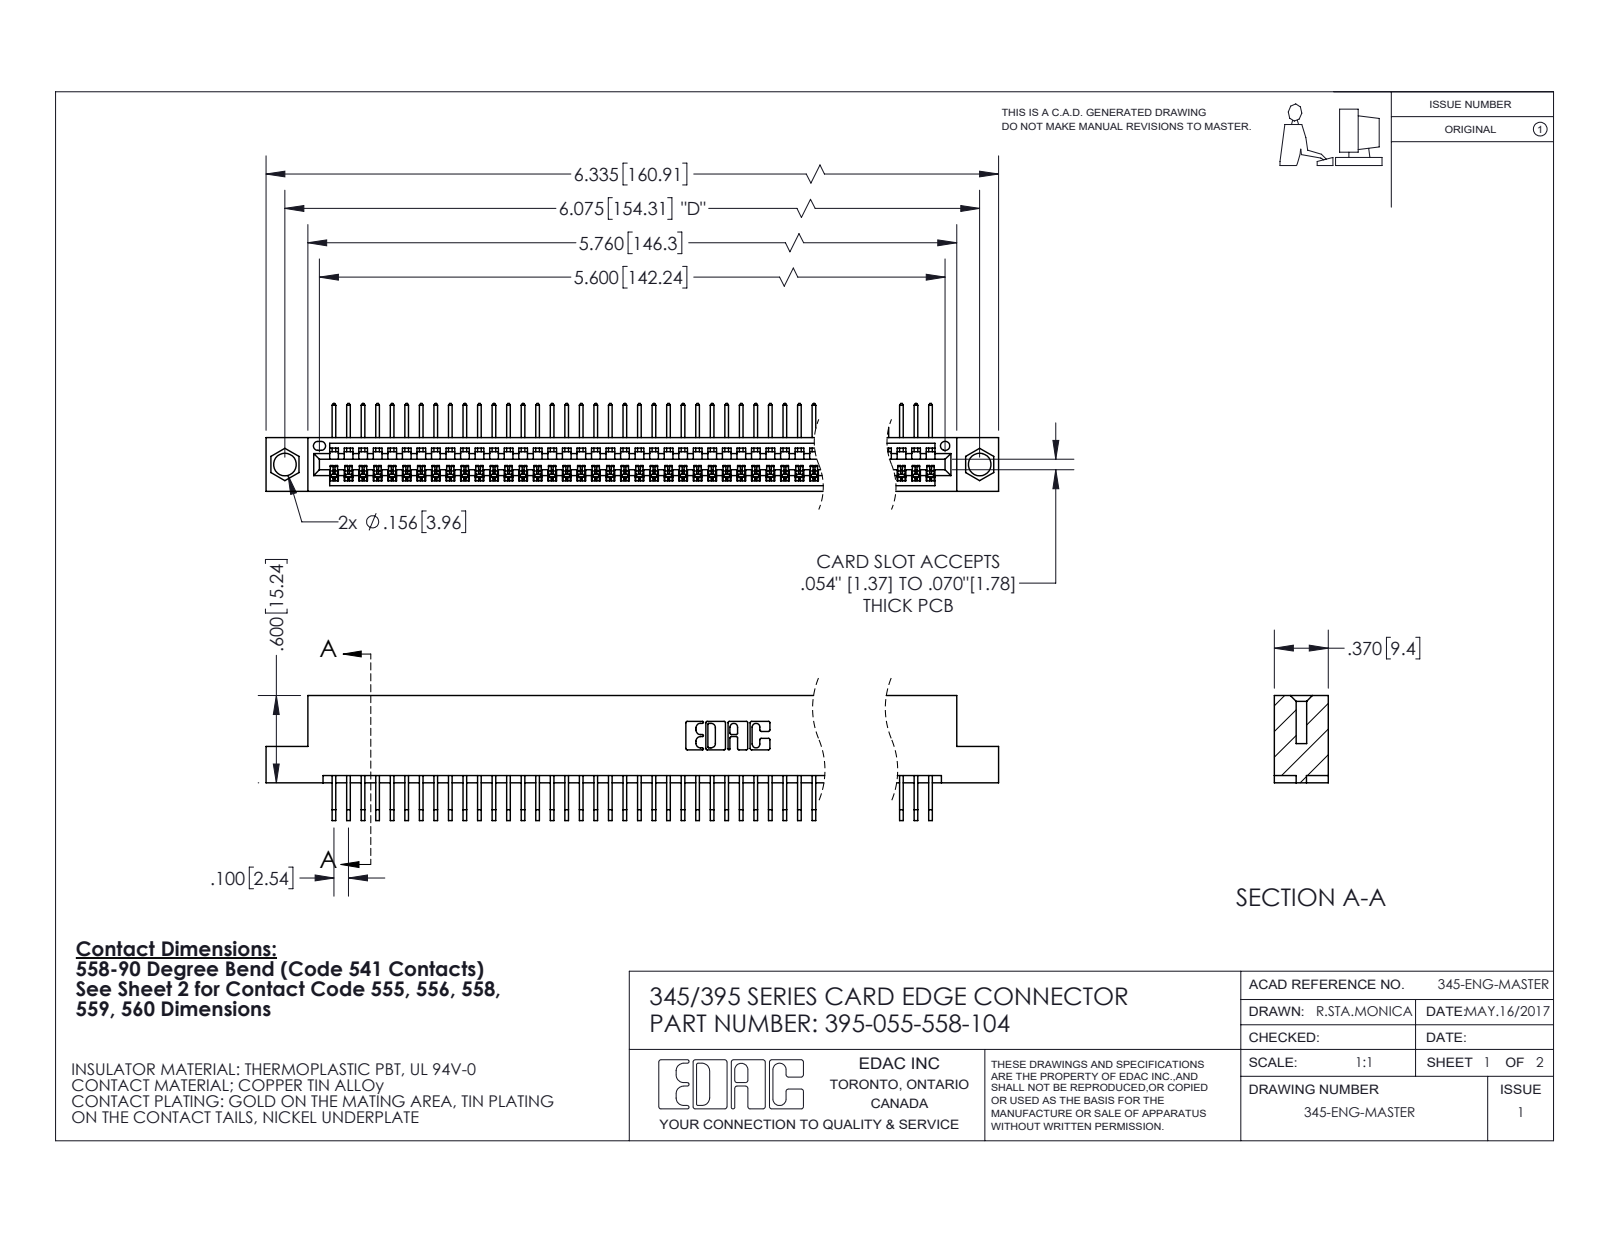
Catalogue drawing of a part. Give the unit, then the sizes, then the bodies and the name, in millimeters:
Units: millimetres
Overall size (bounding box): 160.9 × 21.8 × 15.4
Round holes (diameter × count): ⌀4 ×2, ⌀1.6 ×1
Partial cylindrical surfaces — rounded edges, fillets, slot ends (radius × count): R0.2 ×110, R0.3 ×22, R0.2 ×6, R0.8 ×6, R0.7 ×3, R0.8 ×2, R1 ×2, R0.4 ×1
Main face-to-face distances: 1.8, 7.6, 9.4, 5.1, 2.5, 6.9, 0.6, 5.7, 3.8, 1.8
Hole centre spacings: 6.9, 148.3, 154.3
Volume: 15 500 mm³ · Surface area: 21 650 mm²
Bodies: 56 solids, 3440 faces (2404 planar, 1036 cylindrical, 0 other)
Part name (STEP PRODUCT): 345-292-001_558 Tail - 2; 395-055-558-104; 345 Part_Flush Mounting Lugs - 0.156 Dia-TI
STEP written by: SolidWorks 2020 (CONFIG_CONTROL_DESIGN)
